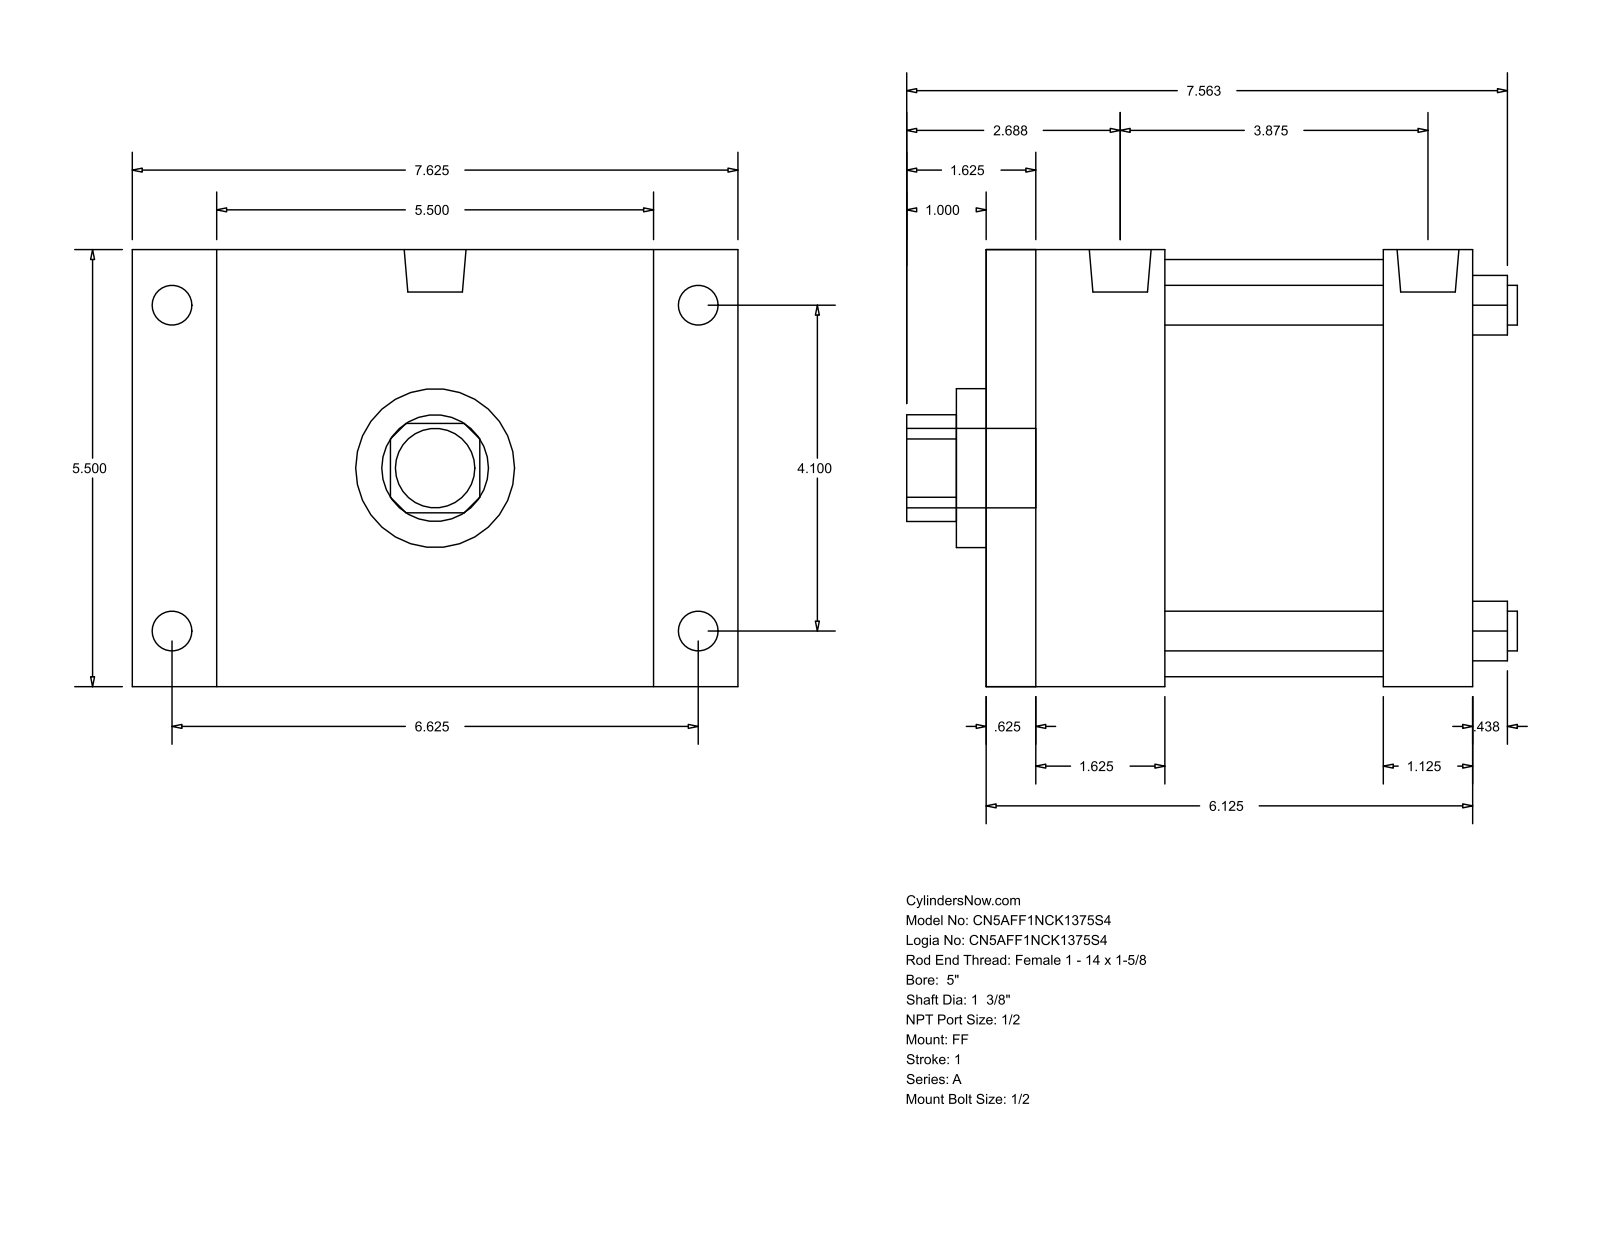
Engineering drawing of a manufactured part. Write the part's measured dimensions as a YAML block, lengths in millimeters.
part_name: "A_FF__0500_1.375"
step_written_by: "GSSL Pune (CONFIG_CONTROL_DESIGN)"
units: millimeters
bodies: {solids: 0, faces: 92, planar: 64, cylindrical: 28, other: 0}
overall_size: [195.26, 193.68, 139.7]
round_holes:
  - {diameter: 12.7, count: 4}
  - {diameter: 34.92, count: 1}
  - {diameter: 50.8, count: 1}
  - {diameter: 133.35, count: 1}
round_bosses_or_shafts:
  - {diameter: 12.7, count: 4}
  - {diameter: 8.73, count: 4}
  - {diameter: 19.77, count: 2}
  - {diameter: 25.4, count: 1}
partial_cylinders:
  - {radius: 17.06, count: 1}
face_to_face_distances: [139.7, 155.57, 15.87, 111.13, 28.57, 69.85, 166.69, 127, 57.15, 41.28]
hole_center_spacings: [73.64, 104.14, 147.28]
